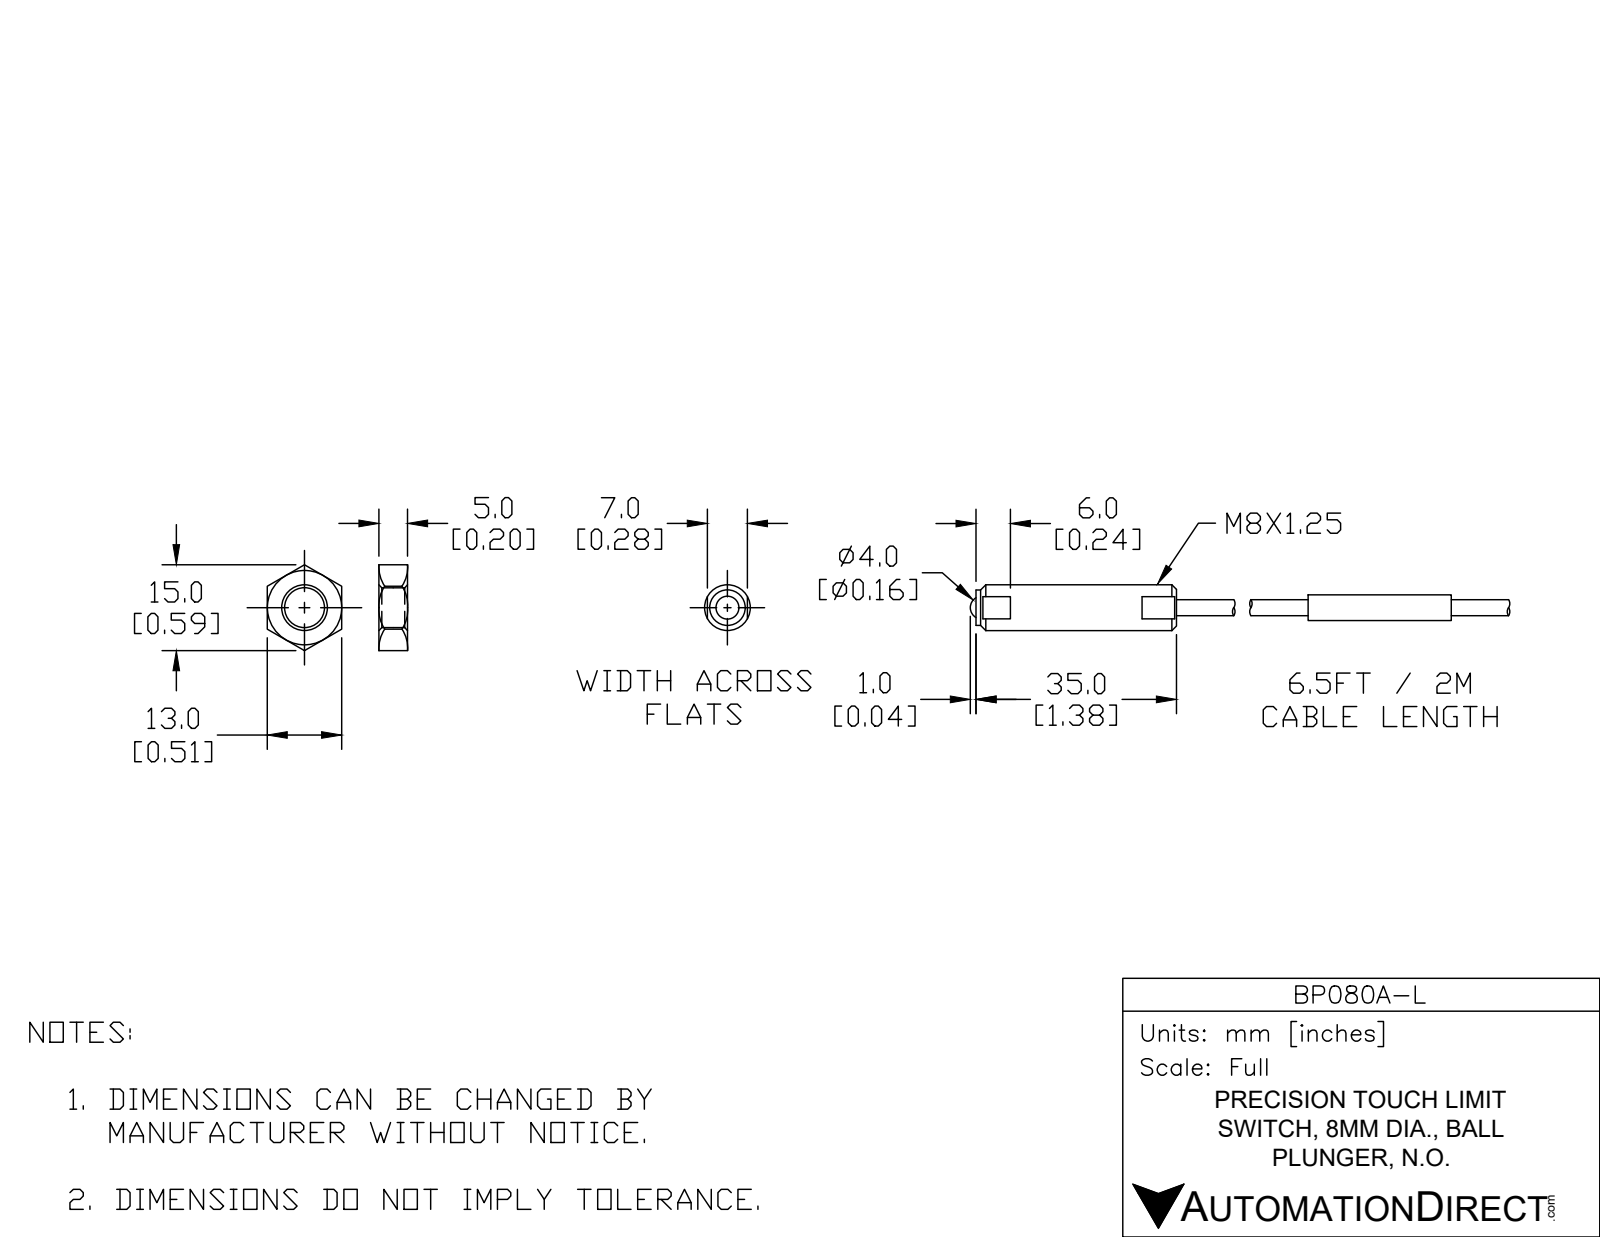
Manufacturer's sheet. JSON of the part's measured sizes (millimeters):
{"part_name": "BP080A-L", "step_written_by": "SolidWorks 2017 (CONFIG_CONTROL_DESIGN)", "units": "millimeters", "bodies": {"solids": 2, "faces": 80, "planar": 7, "cylindrical": 63, "other": 10}, "overall_size": [94, 8, 8], "volume_mm3": 2022, "surface_area_mm2": 2044, "round_bosses_or_shafts": [[8, 1], [6.2, 1], [4.5, 1], [2.8, 1]], "face_to_face_distances": [35, 58, 48, 10, 83, 23, 25, 45, 46, 93]}
